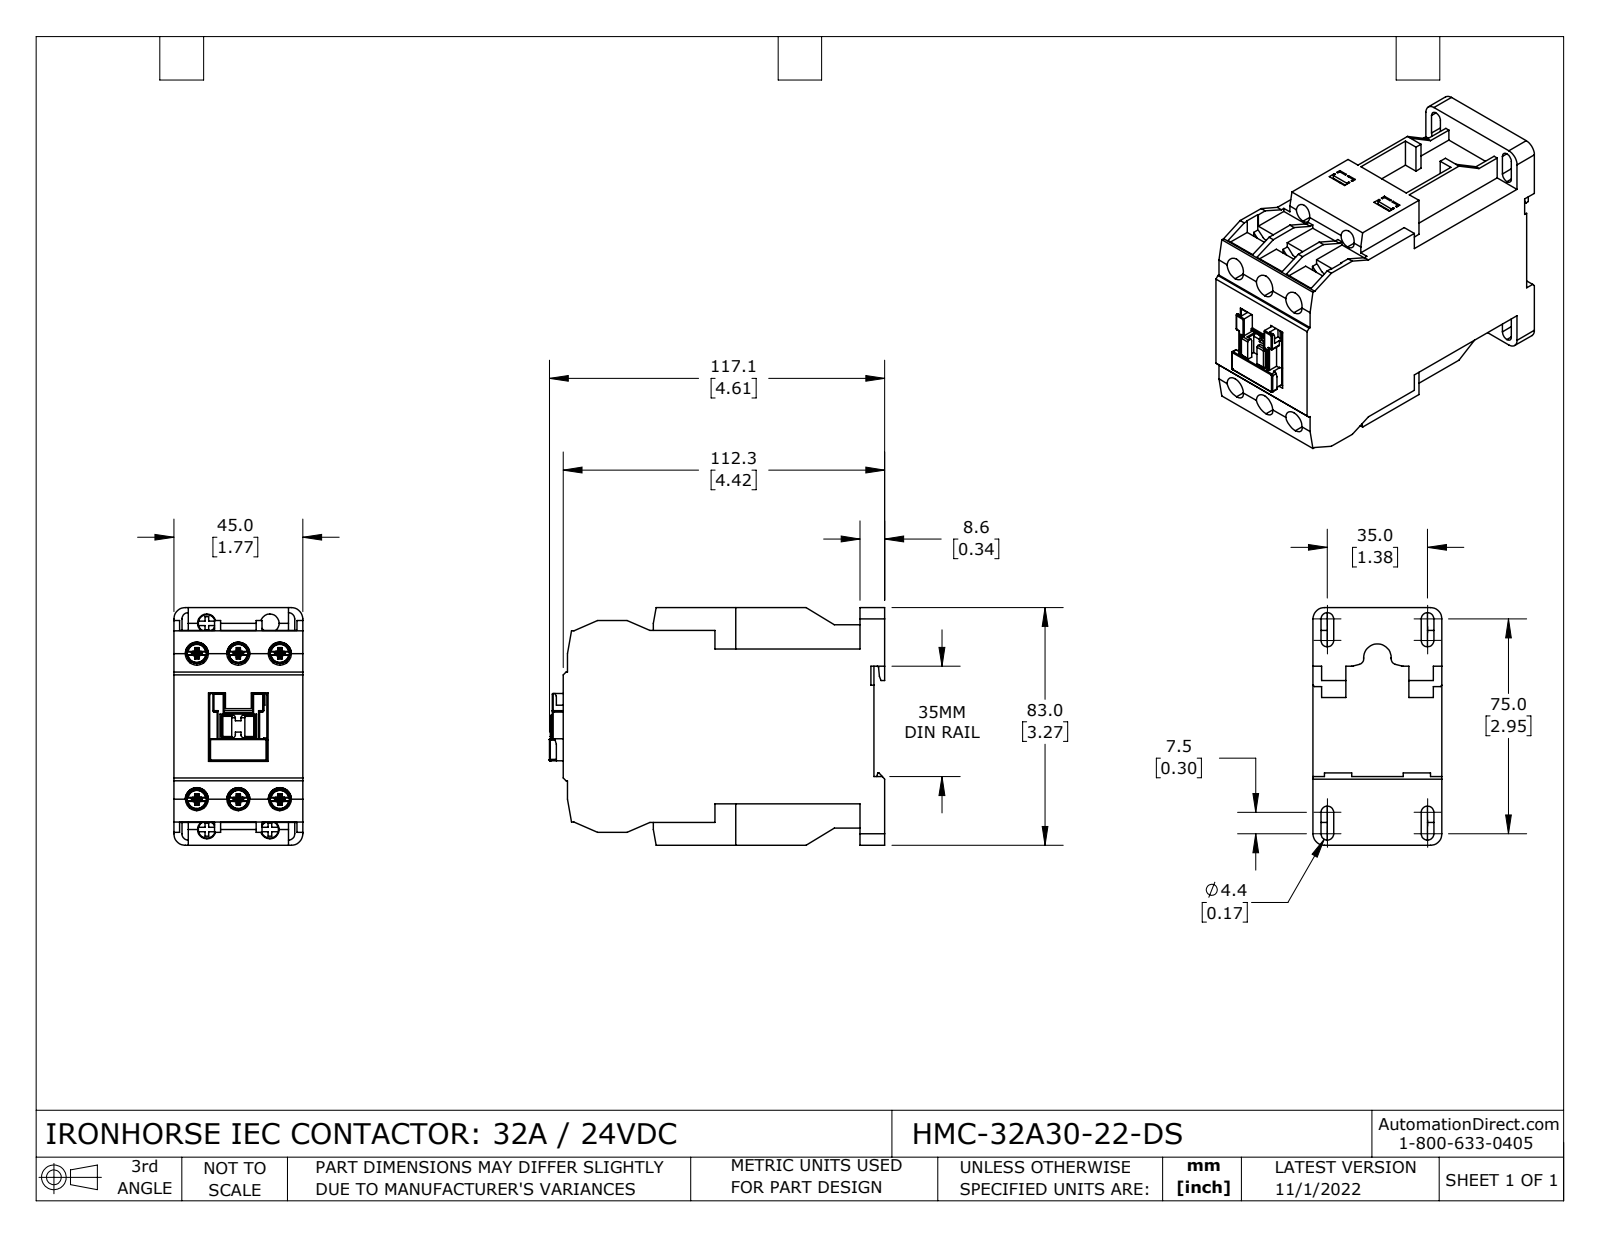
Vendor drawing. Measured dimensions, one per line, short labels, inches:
name: HMC-32A30-22-DS
written by: SolidWorks 2021 (CONFIG_CONTROL_DESIGN)
unit: in
bodies: 18 solids, 1025 faces (652 planar, 169 cylindrical, 204 other)
size: 4.61 × 3.268 × 1.772
volume: 19.81 in³; area: 83.35 in²
holes: 6× ⌀0.204, 6× ⌀0.315, 4× ⌀0.256
bosses: 9× ⌀0.154, 6× ⌀0.134, 3× ⌀0.235, 3× ⌀0.122, 3× ⌀0.091
rounds: 18× R0.02, 13× R0.012, 8× R0.087, 4× R0.039, 4× R0.079, 4× R0.157, 3× R0.151, 3× R0.23
face distances: 1.772, 0.571, 0.189, 0.445, 0.386, 1.386, 0.205, 0.744, 0.366, 0.404
hole spacings: 0.571, 1.142, 2.084, 2.004, 0.436, 0.439, 0.599, 0.602
